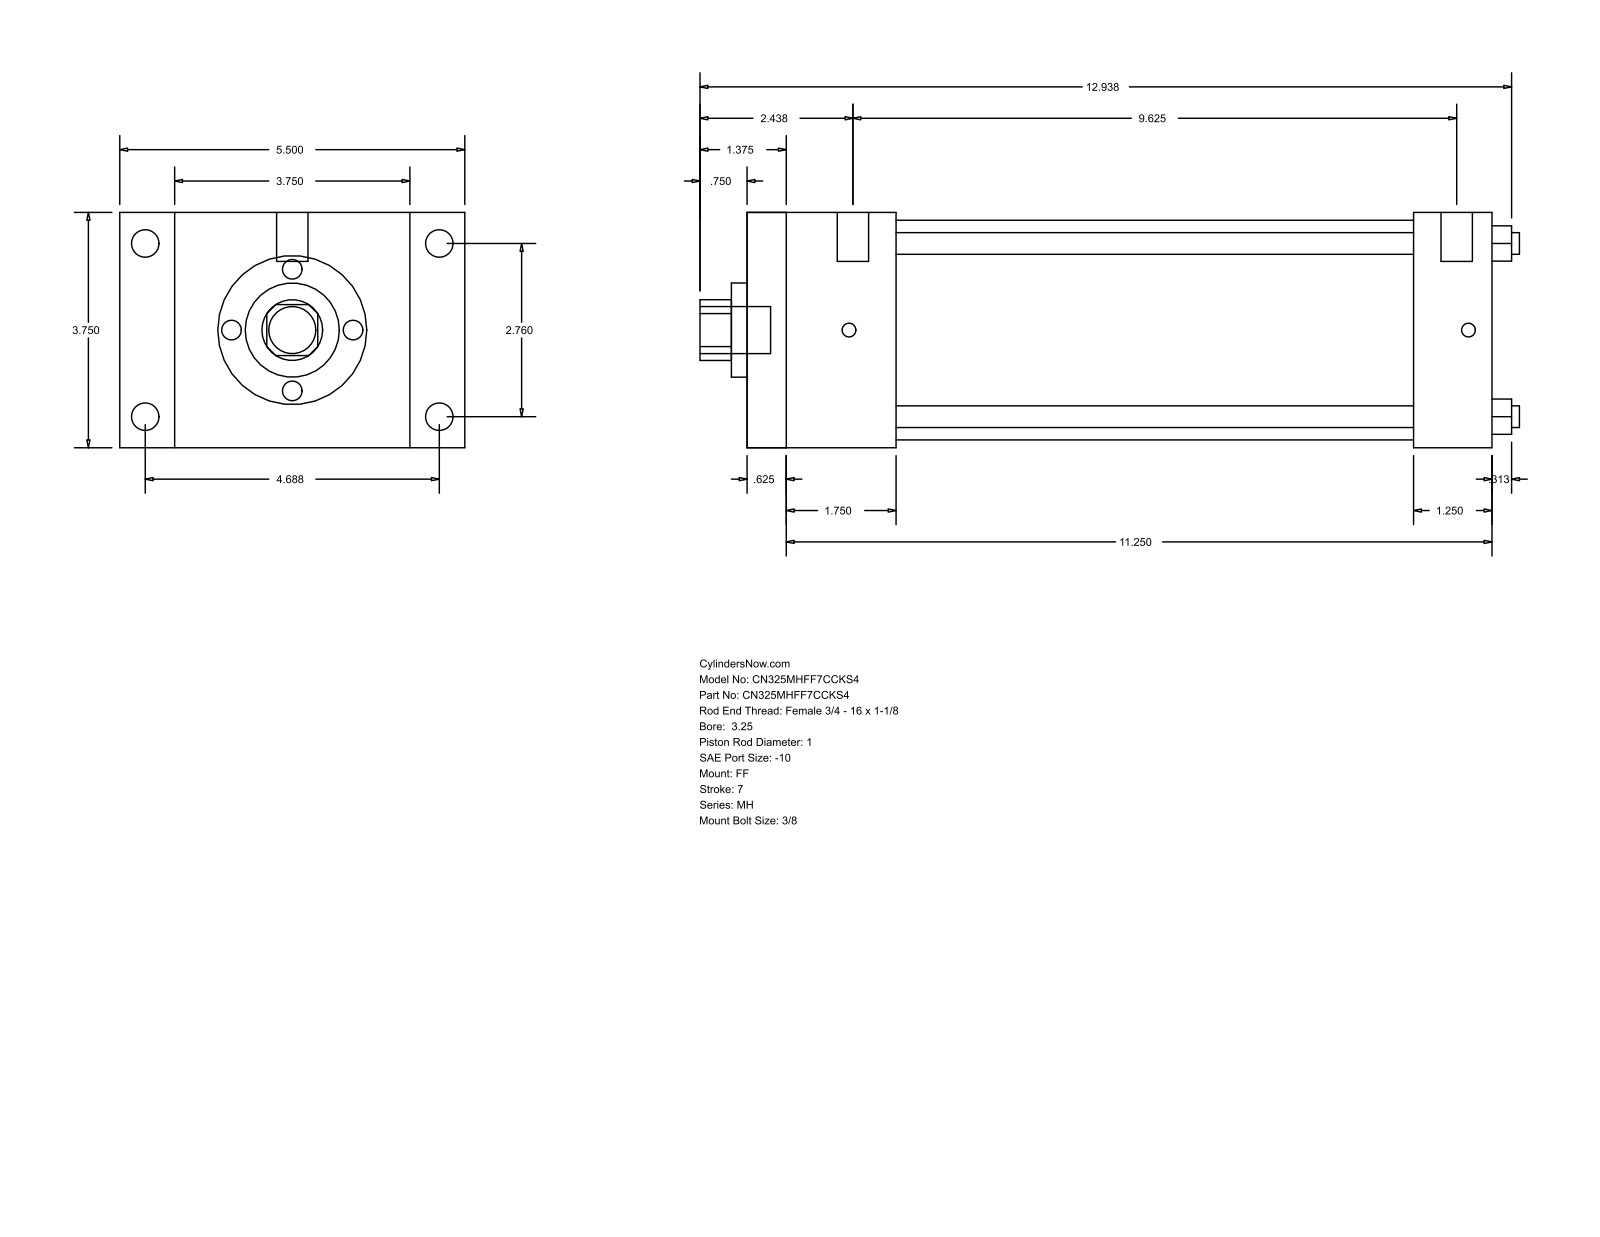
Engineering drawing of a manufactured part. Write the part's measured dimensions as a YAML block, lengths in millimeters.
part_name: "MH_FF__0325_1"
step_written_by: "GSSL Pune (CONFIG_CONTROL_DESIGN)"
units: millimeters
bodies: {solids: 0, faces: 92, planar: 64, cylindrical: 28, other: 0}
overall_size: [331.79, 139.7, 95.25]
round_holes:
  - {diameter: 8.76, count: 4}
  - {diameter: 25.4, count: 1}
  - {diameter: 38.1, count: 1}
  - {diameter: 88.9, count: 1}
round_bosses_or_shafts:
  - {diameter: 11.13, count: 4}
  - {diameter: 5.56, count: 4}
  - {diameter: 12.7, count: 2}
  - {diameter: 19.05, count: 1}
partial_cylinders:
  - {radius: 12.29, count: 1}
face_to_face_distances: [95.24, 301.63, 15.87, 285.76, 22.23, 117.47, 269.88, 254.01, 31.75, 60.33]
hole_center_spacings: [49.57, 70.1, 99.14]
